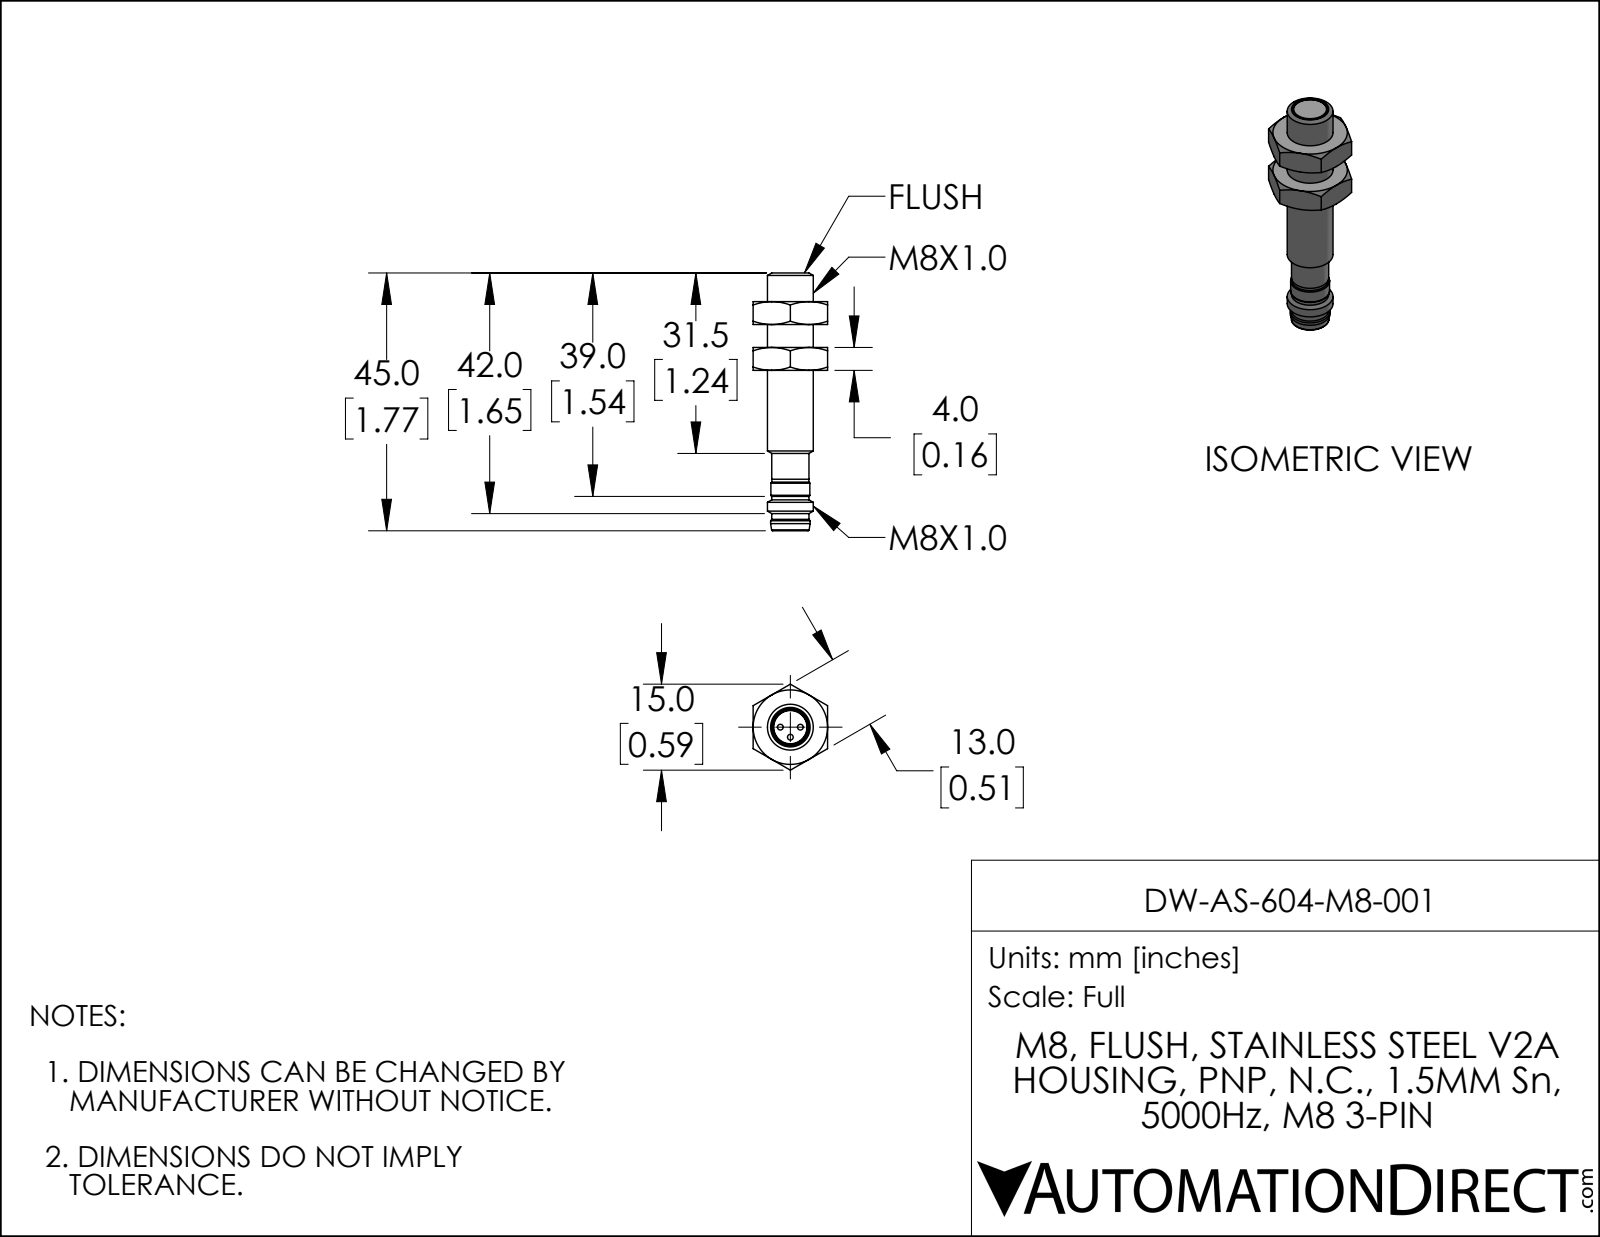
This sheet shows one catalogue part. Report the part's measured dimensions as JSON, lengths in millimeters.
{"part_name": "DW-AS-604-M8-001", "step_written_by": "SolidWorks 2019 (AUTOMOTIVE_DESIGN)", "units": "millimeters", "bodies": {"solids": 1, "faces": 77, "planar": 25, "cylindrical": 14, "other": 38}, "overall_size": [45, 15, 13], "volume_mm3": 2700, "surface_area_mm2": 1839, "round_holes": [[5.8, 1]], "round_bosses_or_shafts": [[1, 3], [8, 1], [6.9, 1], [6.8, 1], [6.5, 1], [6.5, 1]], "face_to_face_distances": [4, 13, 8, 12, 5, 9, 17, 40, 31, 27]}
